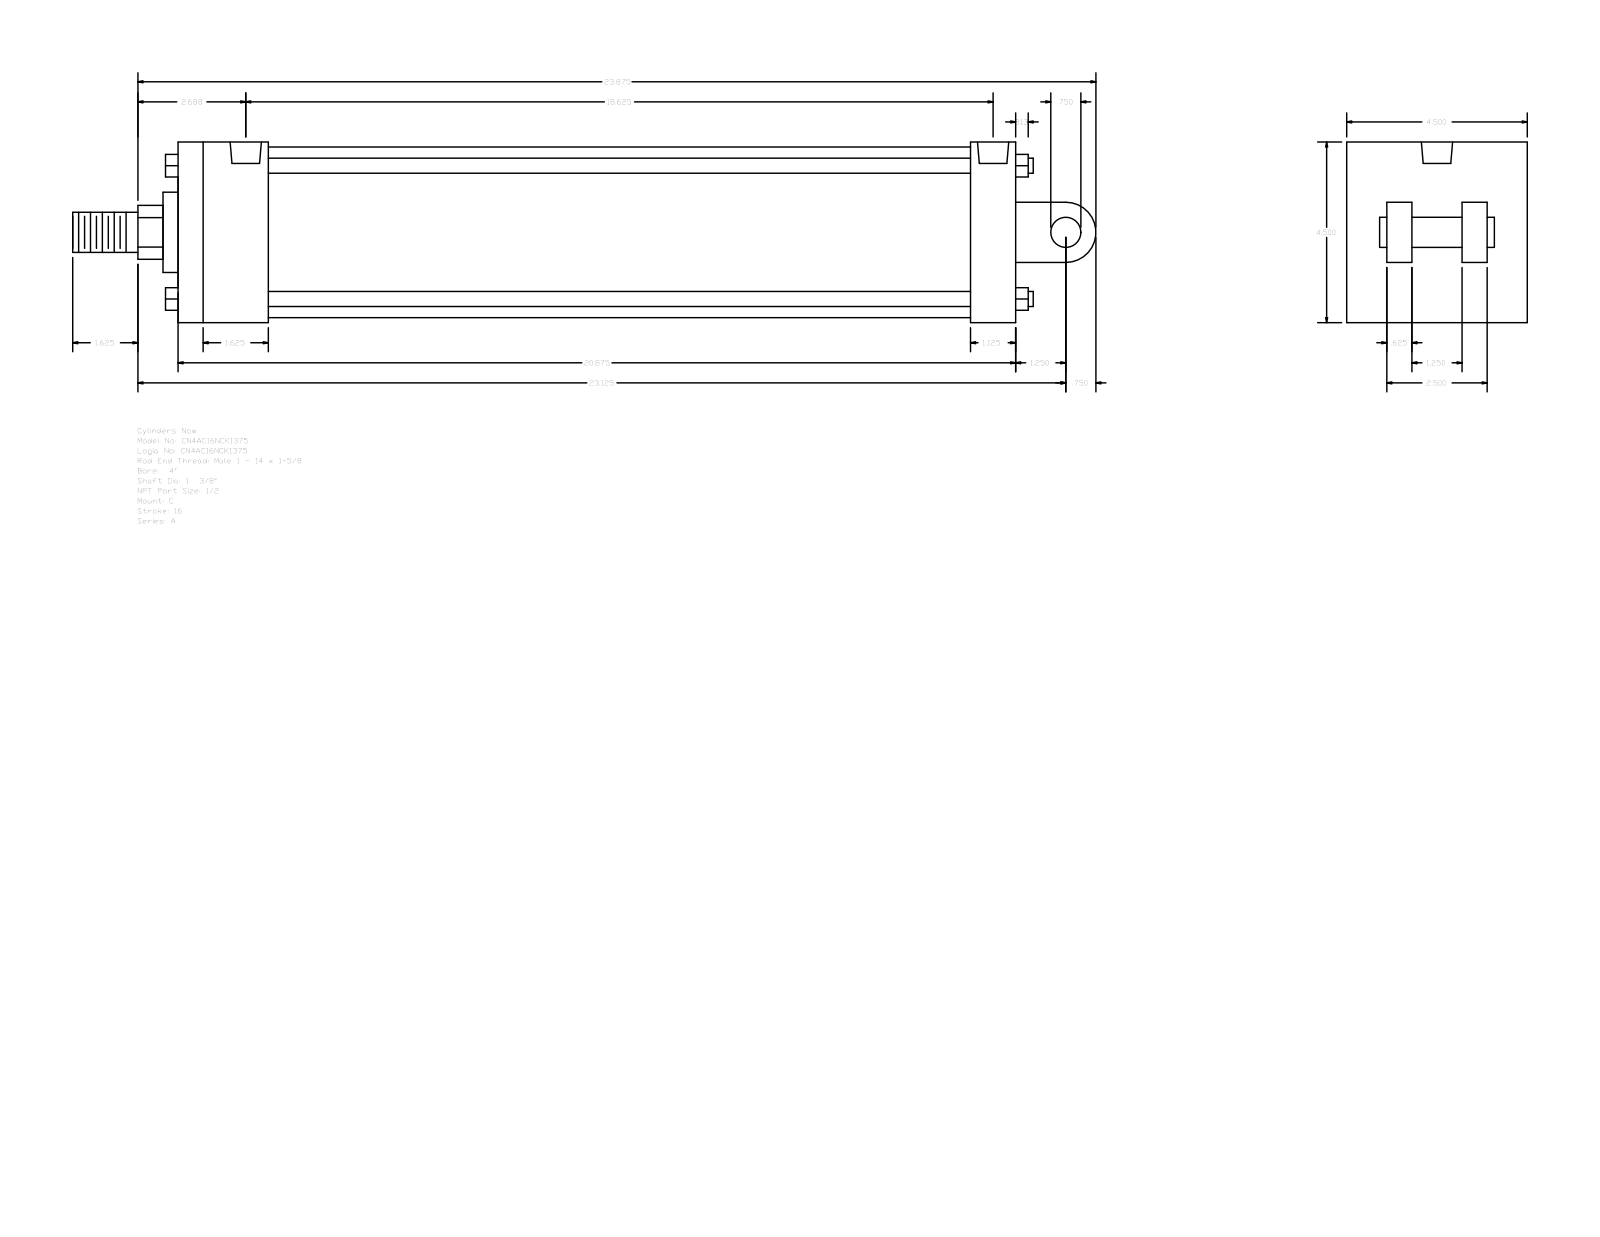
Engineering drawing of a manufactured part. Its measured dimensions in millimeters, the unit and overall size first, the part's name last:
Units: millimetres
Overall size (bounding box): 647.7 × 114.3 × 114.3
Round holes (diameter × count): ⌀8.73 ×4, ⌀19.77 ×2
Round bosses / shafts (diameter × count): ⌀9.53 ×4, ⌀107.95 ×1, ⌀50.8 ×1, ⌀34.92 ×1, ⌀25.4 ×1, ⌀19.05 ×1
Partial cylindrical surfaces — rounded edges, fillets, slot ends (radius × count): R17.06 ×1, R19.05 ×1
Main face-to-face distances: 114.3, 530.22, 57.15, 73.03, 501.65, 28.57, 444.5, 473.07, 41.27, 25.4
Hole centre spacings: 3.18, 466.72, 469.9, 473.08
Bodies: 0 solids, 135 faces (102 planar, 33 cylindrical, 0 other)
Part name (STEP PRODUCT): A_C__0400_1.375
STEP written by: GSSL Pune (CONFIG_CONTROL_DESIGN)
